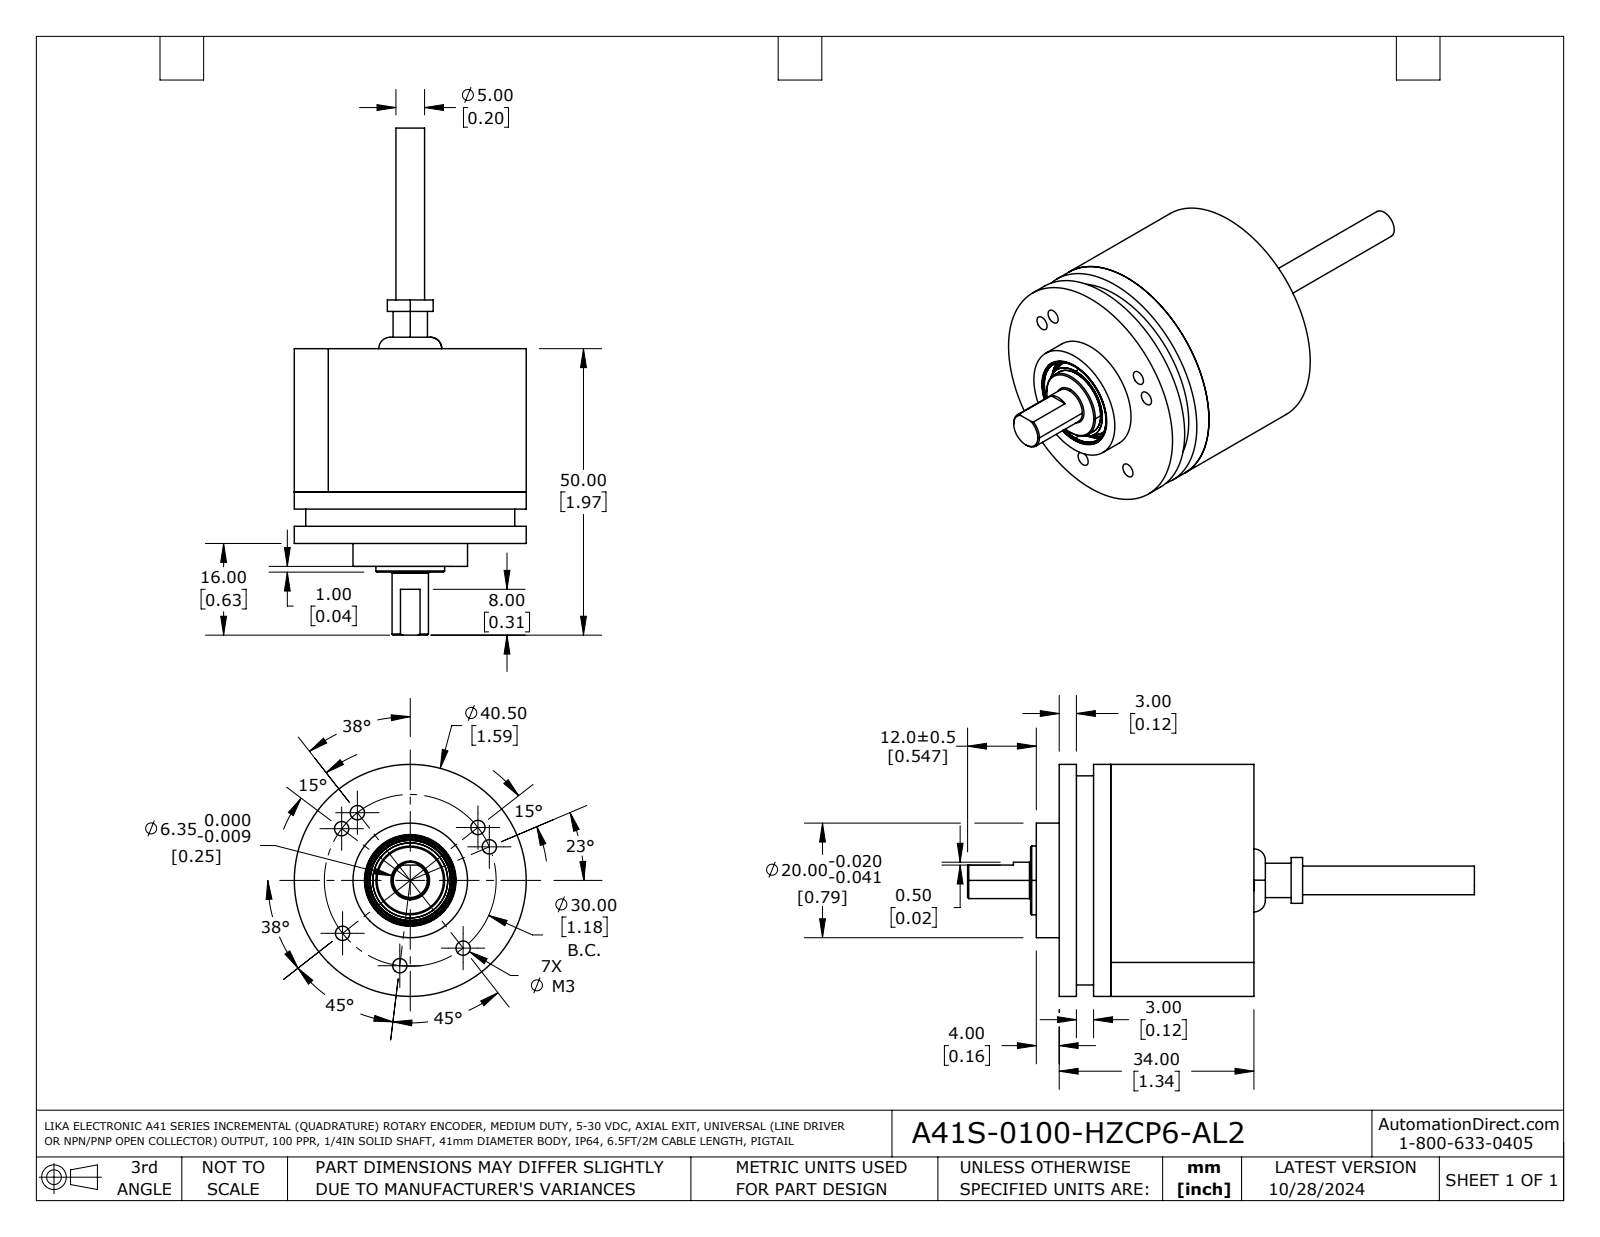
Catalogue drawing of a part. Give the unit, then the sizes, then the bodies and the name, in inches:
Units: inches
Overall size (bounding box): 3.484 × 1.594 × 1.594
Round holes (diameter × count): ⌀0.063 ×7, ⌀0.098 ×7, ⌀0.157 ×3, ⌀0.087 ×2, ⌀0.169 ×1, ⌀0.295 ×1, ⌀0.512 ×1, ⌀0.602 ×1, ⌀0.612 ×1, ⌀0.63 ×1, ⌀1.516 ×1
Round bosses / shafts (diameter × count): ⌀0.079 ×2, ⌀1.594 ×1, ⌀1.496 ×1, ⌀1.457 ×1, ⌀1.437 ×1, ⌀0.787 ×1, ⌀0.472 ×1, ⌀0.315 ×1
Partial cylindrical surfaces — rounded edges, fillets, slot ends (radius × count): R0.039 ×14, R0.007 ×6, R0.008 ×2
Main face-to-face distances: 0.118, 1.339, 0.433, 0.906, 1.22, 0.079, 0.866, 0.984, 0.787, 0.039
Hole centre spacings: 0.591, 0.669, 0.835, 0.11, 0.118, 0.837, 0.945, 1.257
Volume: 1.175 in³ · Surface area: 28.29 in²
Bodies: 11 solids, 422 faces (76 planar, 145 cylindrical, 201 other)
Part name (STEP PRODUCT): A41S-0100-HZCP6-AL2
STEP written by: SolidWorks 2021 (AUTOMOTIVE_DESIGN)
